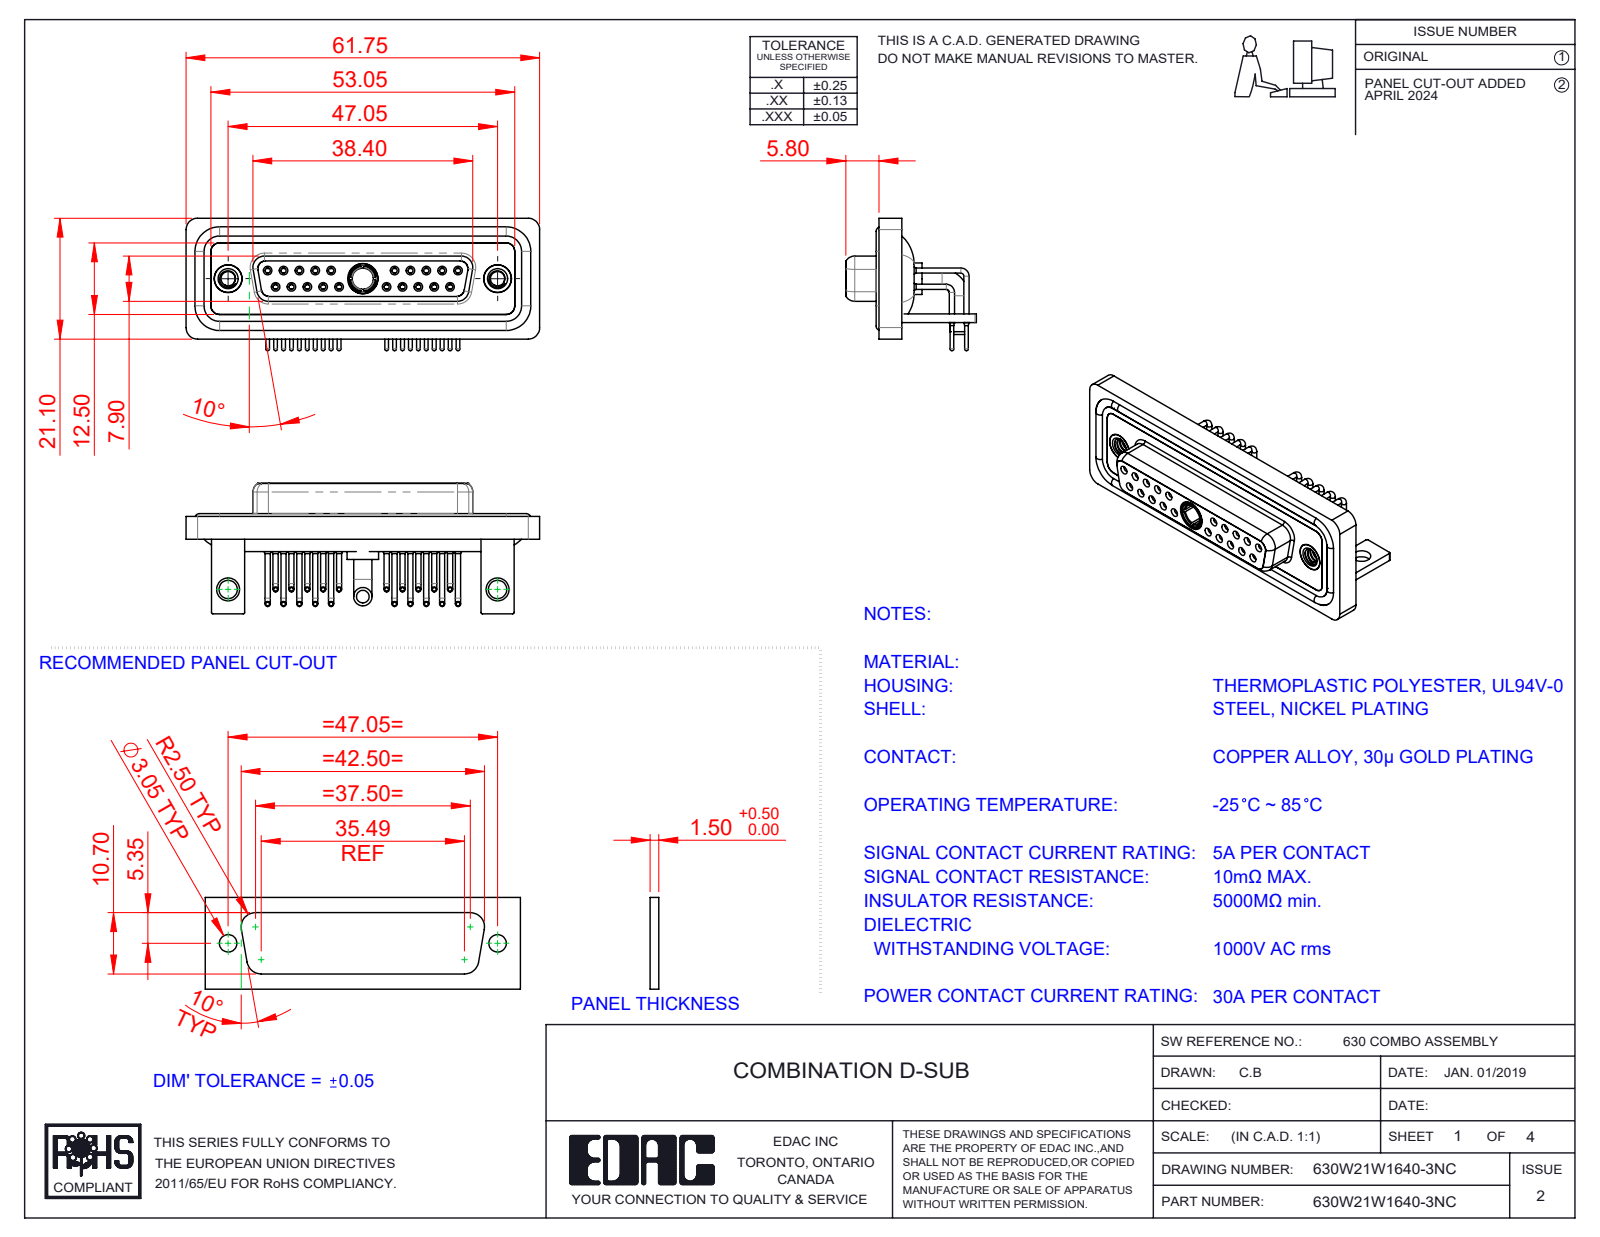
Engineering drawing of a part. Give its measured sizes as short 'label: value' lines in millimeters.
name: 630Combo Stabilizer Bracket_50 Contacts; 630Combo Shell Front_25 Contacts; 630Combo Contact Row 2_50 Contacts; 630Combo Threaded Rivet_A (+6 more)
written by: SolidWorks 2023 (CONFIG_CONTROL_DESIGN)
unit: mm
bodies: 31 solids, 1566 faces (454 planar, 695 cylindrical, 417 other)
size: 61.75 × 23.12 × 22.8
volume: 8 893 mm³; area: 15 537 mm²
holes: 20× ⌀0.9, 20× ⌀1.1, 20× ⌀1.5, 20× ⌀2, 10× ⌀1.6, 10× ⌀1.7, 3× ⌀4.85, 2× ⌀2.5, 2× ⌀3.2, 2× ⌀4, 2× ⌀4.05, 2× ⌀5
bosses: 20× ⌀0.9, 20× ⌀0.65, 14× ⌀1.6, 2× ⌀4.95, 2× ⌀4.8, 2× ⌀3.2, 1× ⌀5.5, 1× ⌀5.2
rounds: 19× R2, 18× R1.5, 16× R0.25, 8× R1.35, 8× R1.6, 5× R0.5, 4× R0.6, 4× R0.65
face distances: 0.4, 1.8, 2.9, 3.7, 1.5, 4.1, 1.1, 1.4, 1.6, 2.5
hole spacings: 3.16, 2.77, 5.54, 8.31, 5.04, 19.39, 20.97, 22.16
